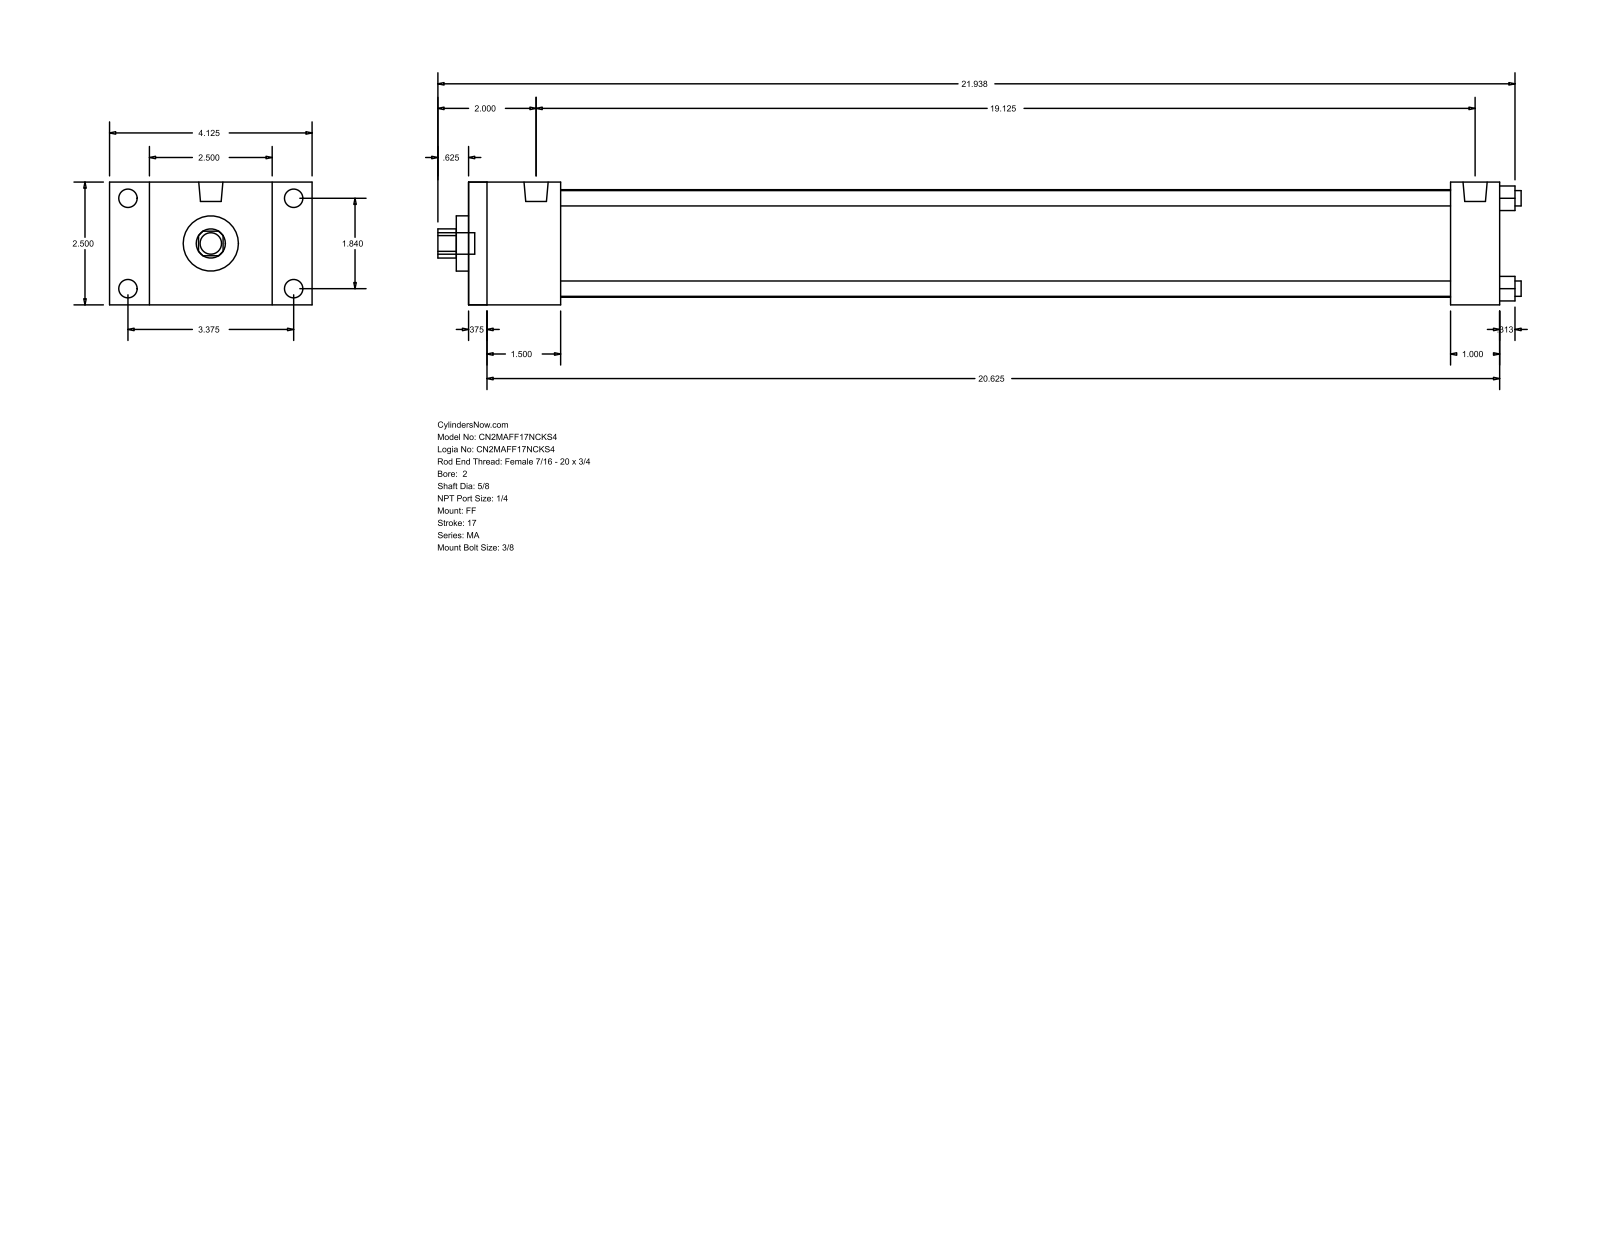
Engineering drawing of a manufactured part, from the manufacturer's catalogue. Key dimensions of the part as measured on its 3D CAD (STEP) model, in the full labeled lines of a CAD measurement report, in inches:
Part name (STEP PRODUCT): MA_FF__0200_0.625
STEP written by: GSSL Pune (CONFIG_CONTROL_DESIGN)
Units: inches
Bodies: 0 solids, 92 faces (64 planar, 28 cylindrical, 0 other)
Overall size (bounding box): 22.063 × 4.125 × 2.5
Round holes (diameter × count): ⌀0.313 ×4, ⌀0.625 ×1, ⌀1.125 ×1, ⌀2.19 ×1
Round bosses / shafts (diameter × count): ⌀0.375 ×4, ⌀0.313 ×4, ⌀0.492 ×2, ⌀0.437 ×1
Partial cylindrical surfaces — rounded edges, fillets, slot ends (radius × count): R0.297 ×1
Main face-to-face distances: 2.5, 21, 0.375, 20.625, 1.5, 1.875, 20, 19.625, 18.125, 19.125
Hole centre spacings: 1.301, 1.84, 2.602
